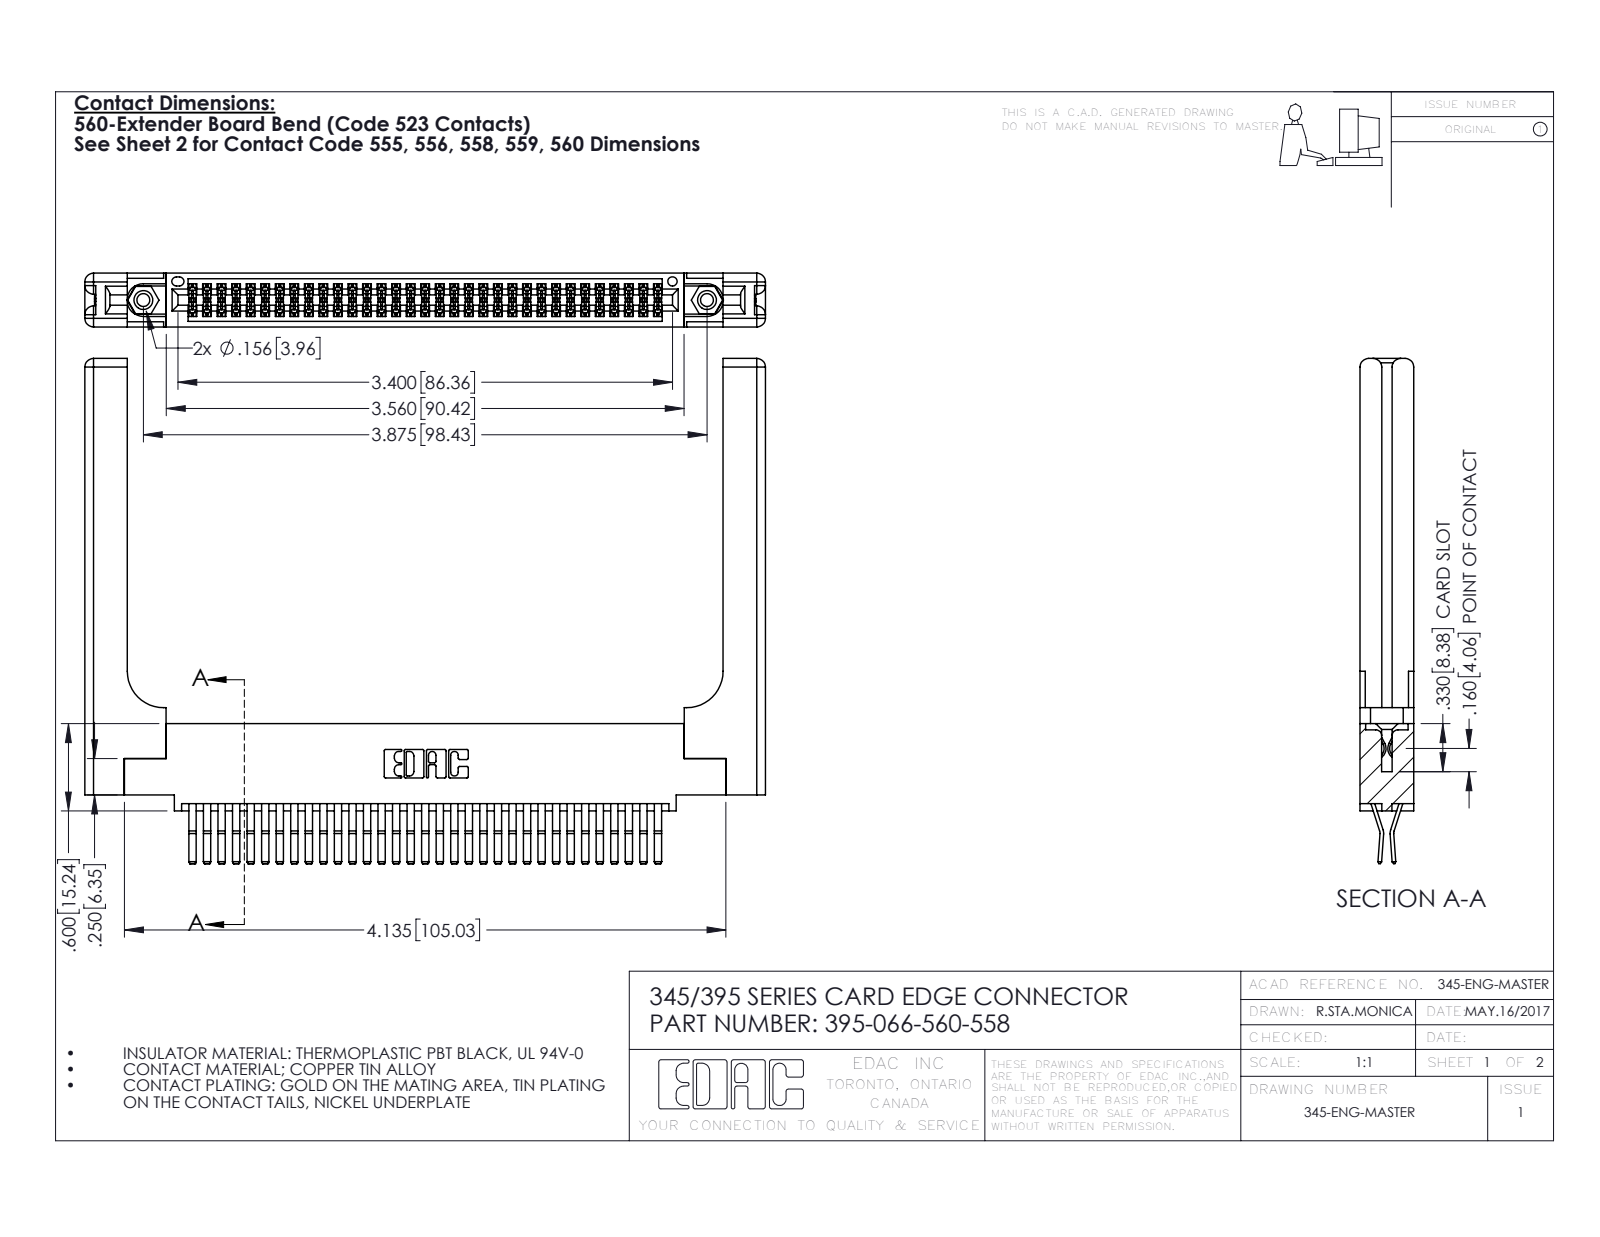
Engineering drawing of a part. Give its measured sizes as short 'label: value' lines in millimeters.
name: 345-220-058_345-220-058; 345-292-001_560 Tail; 395-066-560-558; 345 Part_0.110 Offset - 0.156 Dia-TH (+1 more)
written by: SolidWorks 2016 (CONFIG_CONTROL_DESIGN)
unit: mm
bodies: 71 solids, 3818 faces (2410 planar, 1348 cylindrical, 60 other)
size: 118.8 × 88.2 × 9.4
volume: 20 300 mm³; area: 23 560 mm²
holes: 2× ⌀2.3, 2× ⌀3.2, 2× ⌀4, 1× ⌀1.6
bosses: 2× ⌀3.9
rounds: 100× R0.2, 22× R0.3, 16× R1.5, 6× R0.2, 6× R0.8, 3× R0.7, 2× R0.3, 2× R0.4
face distances: 9.4, 1.8, 7.6, 0.6, 2.5, 6.9, 5.1, 5.7, 3.8, 3.8
hole spacings: 6.9, 92.5, 98.4
